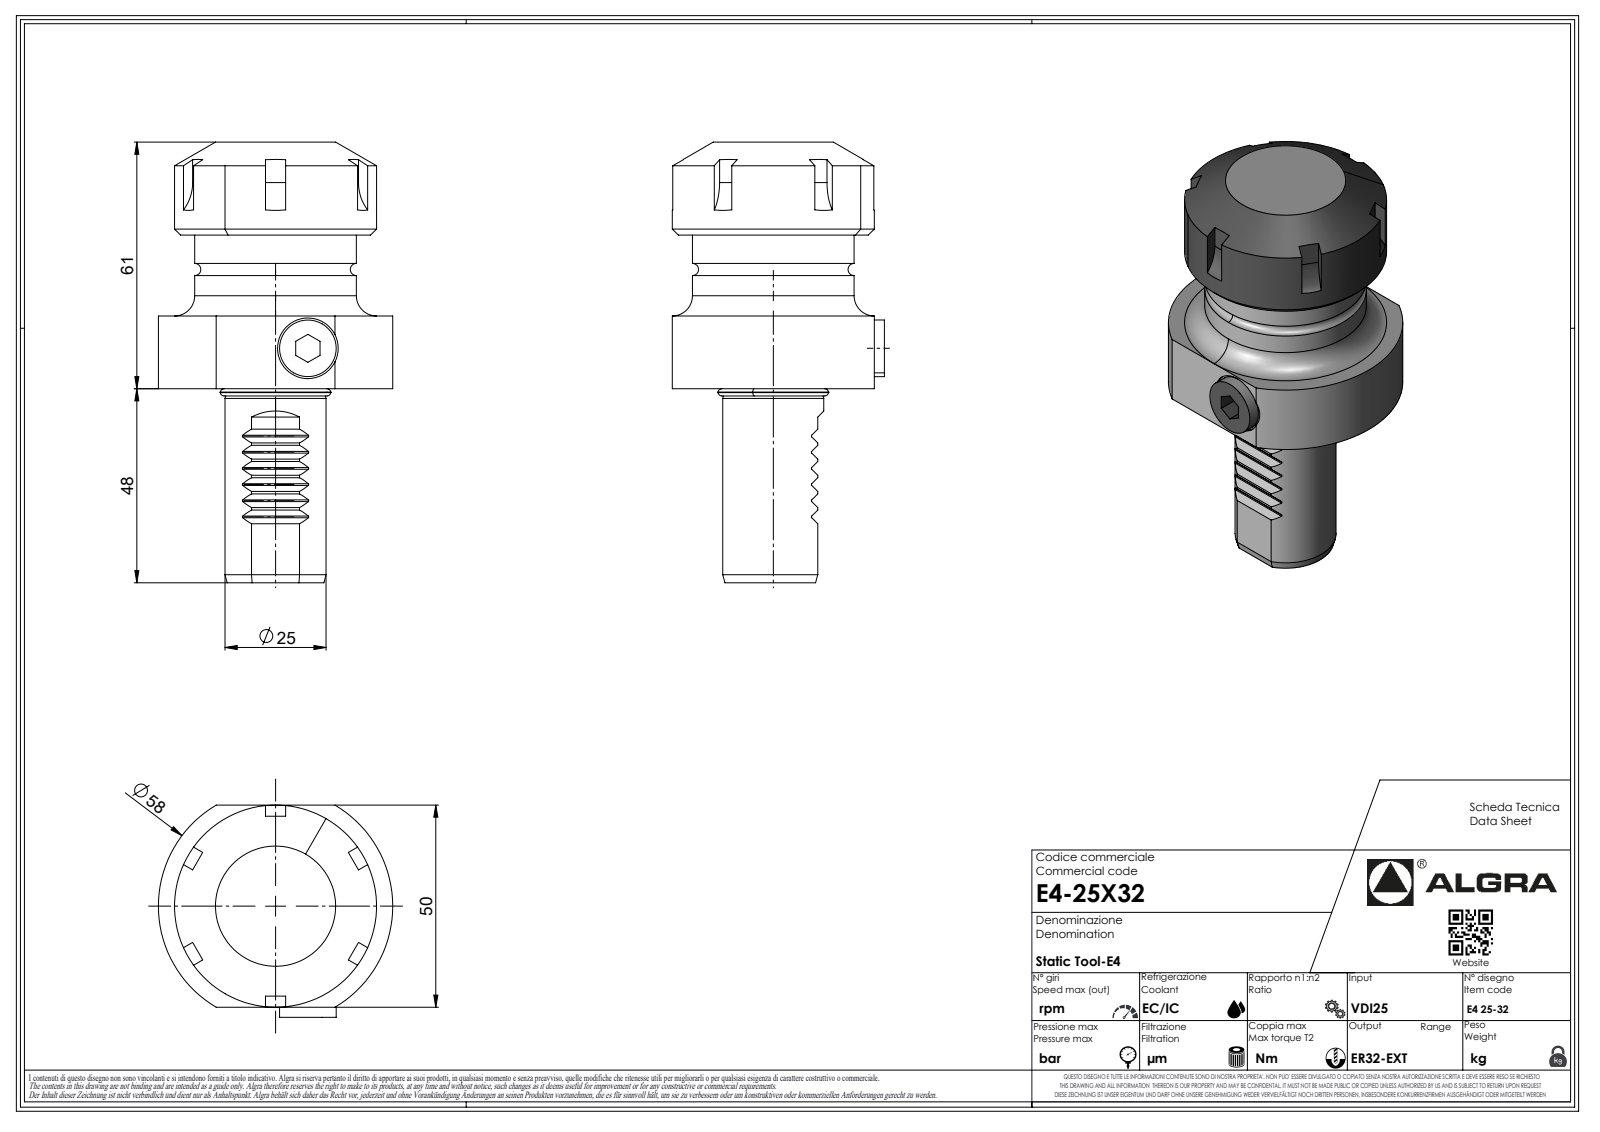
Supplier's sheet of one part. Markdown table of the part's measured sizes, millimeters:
| quantity | value |
| --- | --- |
| part name | E425X32 |
| STEP written by | SolidWorks 2023 (AUTOMOTIVE_DESIGN) |
| units | millimeters |
| bodies | 1 solid, 91 faces (59 planar, 21 cylindrical, 11 other) |
| overall size | 109 × 58 × 52.5 |
| volume | 133 376 mm³ |
| surface area | 19 426 mm² |
| round holes (diameter × count) | 15 × 1 |
| round bosses / shafts (diameter × count) | 50 × 1, 40 × 1, 27.47 × 1, 25 × 1, 14 × 1 |
| partial cylindrical surfaces (radius × count) | 0.3 × 6, 10 × 6, 29 × 1 |
| main face-to-face distances | 61, 43, 18, 23, 20, 38, 109, 86, 66, 48 |
